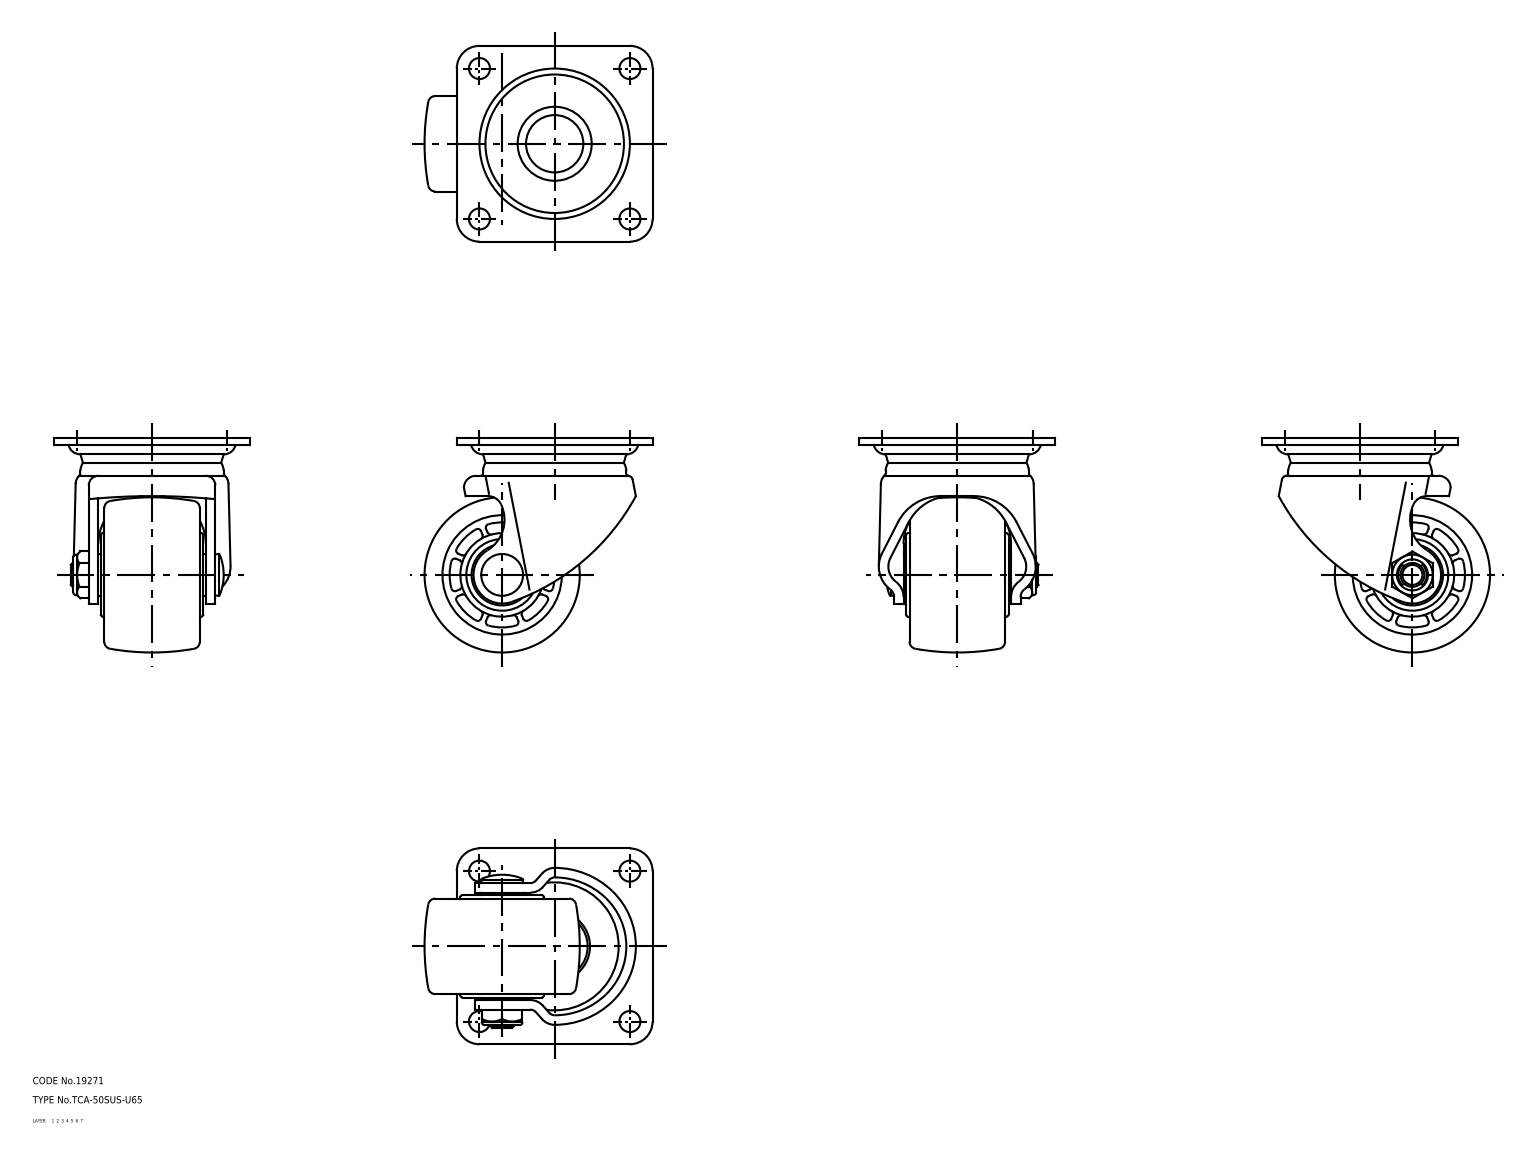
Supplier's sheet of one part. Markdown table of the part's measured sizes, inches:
| quantity | value |
| --- | --- |
| part name | 67131492; 67131505; 67131518; 67131531 (+3 more) |
| STEP written by | CADfix (AUTOMOTIVE_DESIGN) |
| units | inches |
| bodies | 7 solids, 332 faces (0 planar, 0 cylindrical, 332 other) |
| overall size | 3.76 × 3.543 × 3.228 |
| volume | 12.57 in³ |
| surface area | 113.4 in² |
